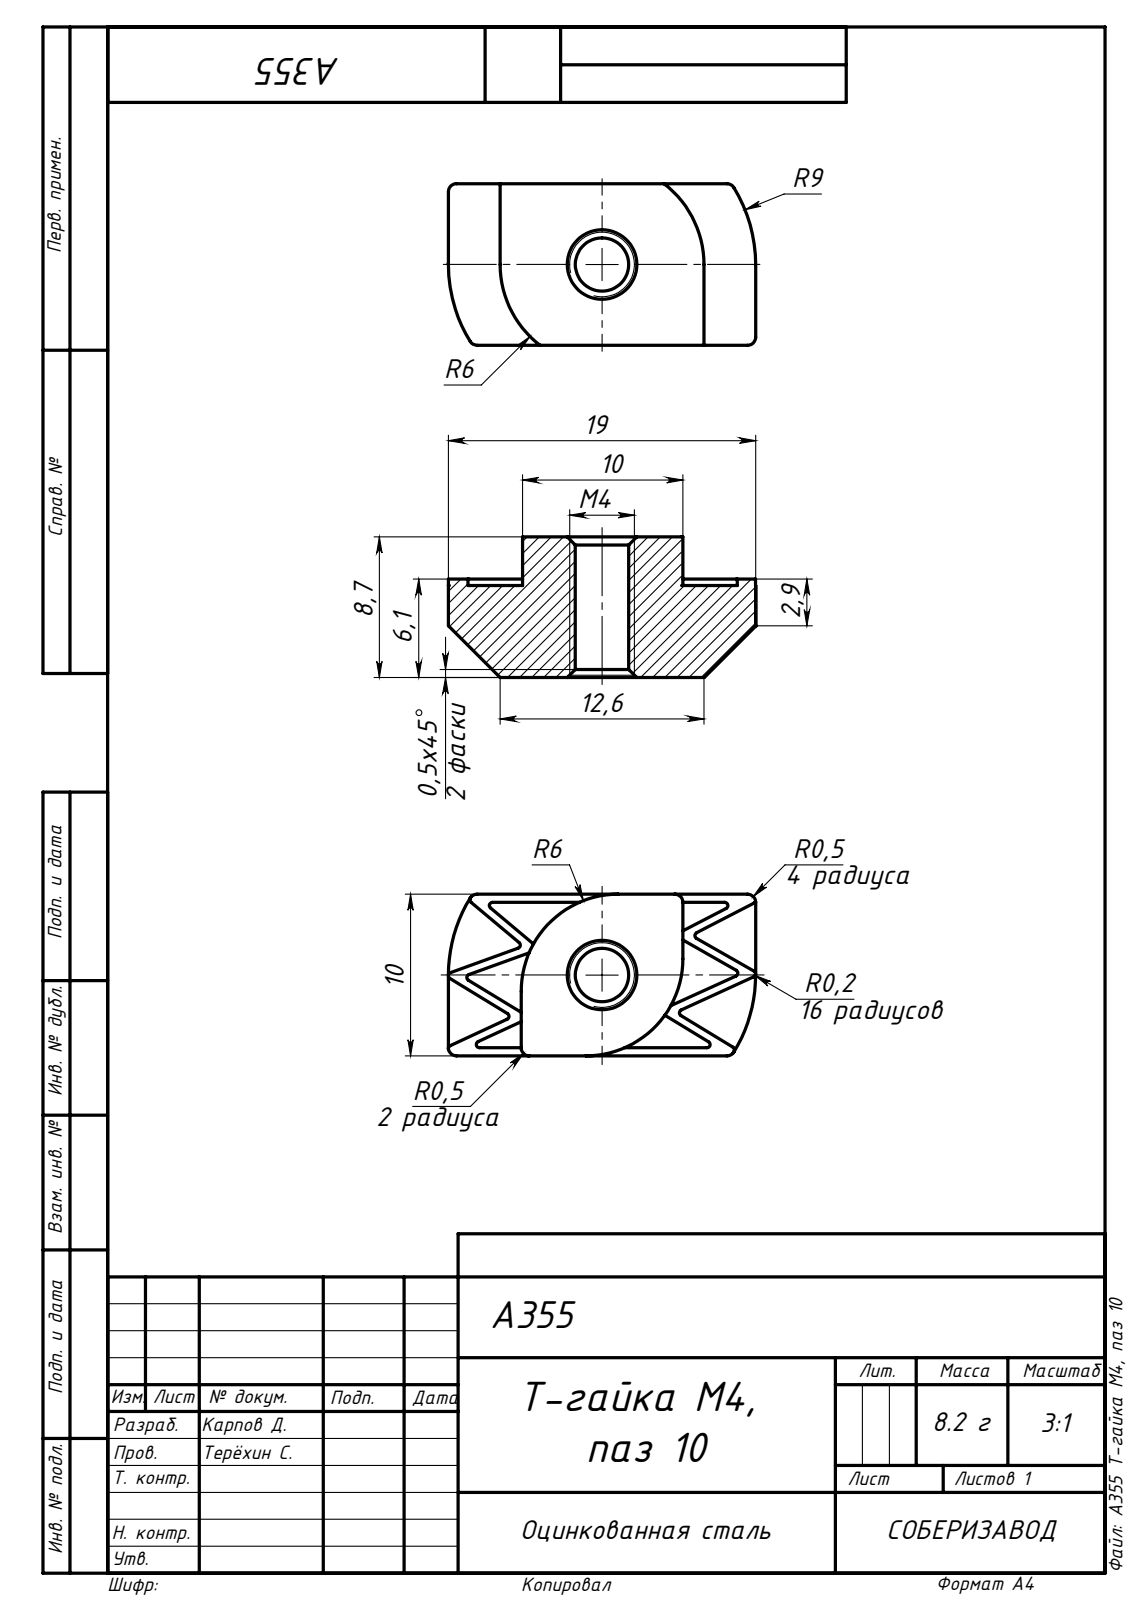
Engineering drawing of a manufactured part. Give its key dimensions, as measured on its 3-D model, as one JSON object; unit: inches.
{"part_name": "A355 Т-гайка М4, паз 10", "step_written_by": "SolidWorks 2018 (AUTOMOTIVE_DESIGN)", "units": "inches", "bodies": {"solids": 1, "faces": 78, "planar": 44, "cylindrical": 28, "other": 6}, "overall_size": [0.748, 0.394, 0.343], "volume_in3": 0.069, "surface_area_in2": 1.3, "round_holes": [[0.13, 1]], "partial_cylinders_radius": [[0.008, 16], [0.02, 6], [0.236, 2], [0.357, 2]], "face_to_face_distances": [0.394, 0.343, 0.224, 0.118, 0.24, 0.016, 0.102, 0.177, 0.571, 0.02]}
